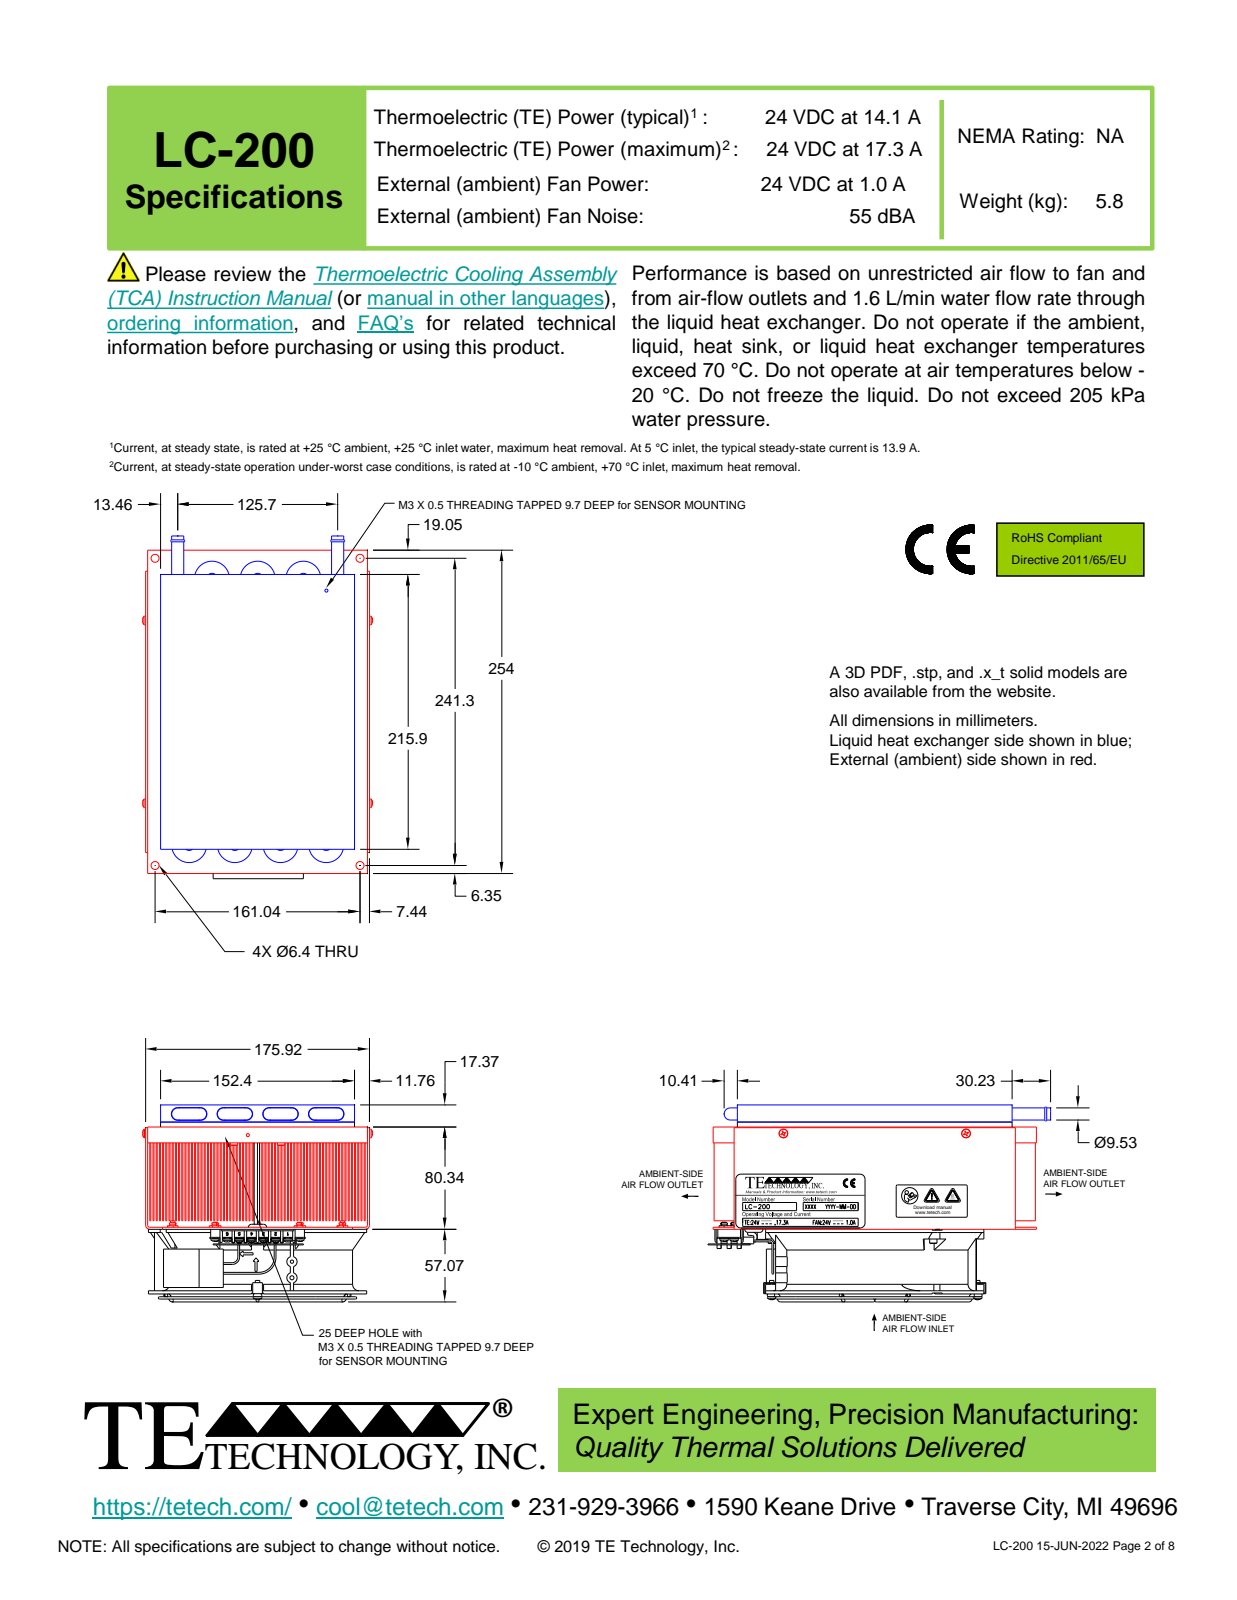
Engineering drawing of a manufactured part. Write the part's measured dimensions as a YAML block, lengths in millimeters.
part_name: "heat sink LC-200; 7514 exchanger plate; 2391 elbow; 2352-01 inlet (+8 more)"
step_written_by: "Alibre (AUTOMOTIVE_DESIGN)"
units: millimeters
bodies: {solids: 173, faces: 3561, planar: 2215, cylindrical: 562, other: 784}
overall_size: [269.23, 180.8, 154.78]
volume: 2289000
surface_area: 2461000
round_holes:
  - {diameter: 2.64, count: 25}
  - {diameter: 2.65, count: 8}
  - {diameter: 4.17, count: 8}
  - {diameter: 4.22, count: 8}
  - {diameter: 4.27, count: 8}
  - {diameter: 4.78, count: 8}
  - {diameter: 5.56, count: 8}
  - {diameter: 5.84, count: 8}
  - {diameter: 8.41, count: 8}
  - {diameter: 8.61, count: 8}
  - {diameter: 10.01, count: 8}
  - {diameter: 12.7, count: 8}
round_bosses_or_shafts:
  - {diameter: 3.51, count: 31}
  - {diameter: 6.86, count: 22}
  - {diameter: 9.53, count: 17}
  - {diameter: 2.3, count: 16}
  - {diameter: 5.74, count: 11}
  - {diameter: 10.31, count: 8}
  - {diameter: 6.34, count: 8}
  - {diameter: 6.3, count: 8}
partial_cylinders:
  - {radius: 0.95, count: 21}
  - {radius: 0.79, count: 16}
  - {radius: 0.38, count: 8}
  - {radius: 0.76, count: 8}
  - {radius: 0.78, count: 8}
  - {radius: 0.81, count: 8}
  - {radius: 1.98, count: 8}
  - {radius: 1.27, count: 5}
face_to_face_distances: [5.03, 2.51, 10.06, 1.7, 3.33, 7.54, 2.52, 6.73, 0.81, 8.36]
hole_center_spacings: [17.96, 7.87, 25.49, 35.92, 37.08, 51.59, 65.63, 65.84]
